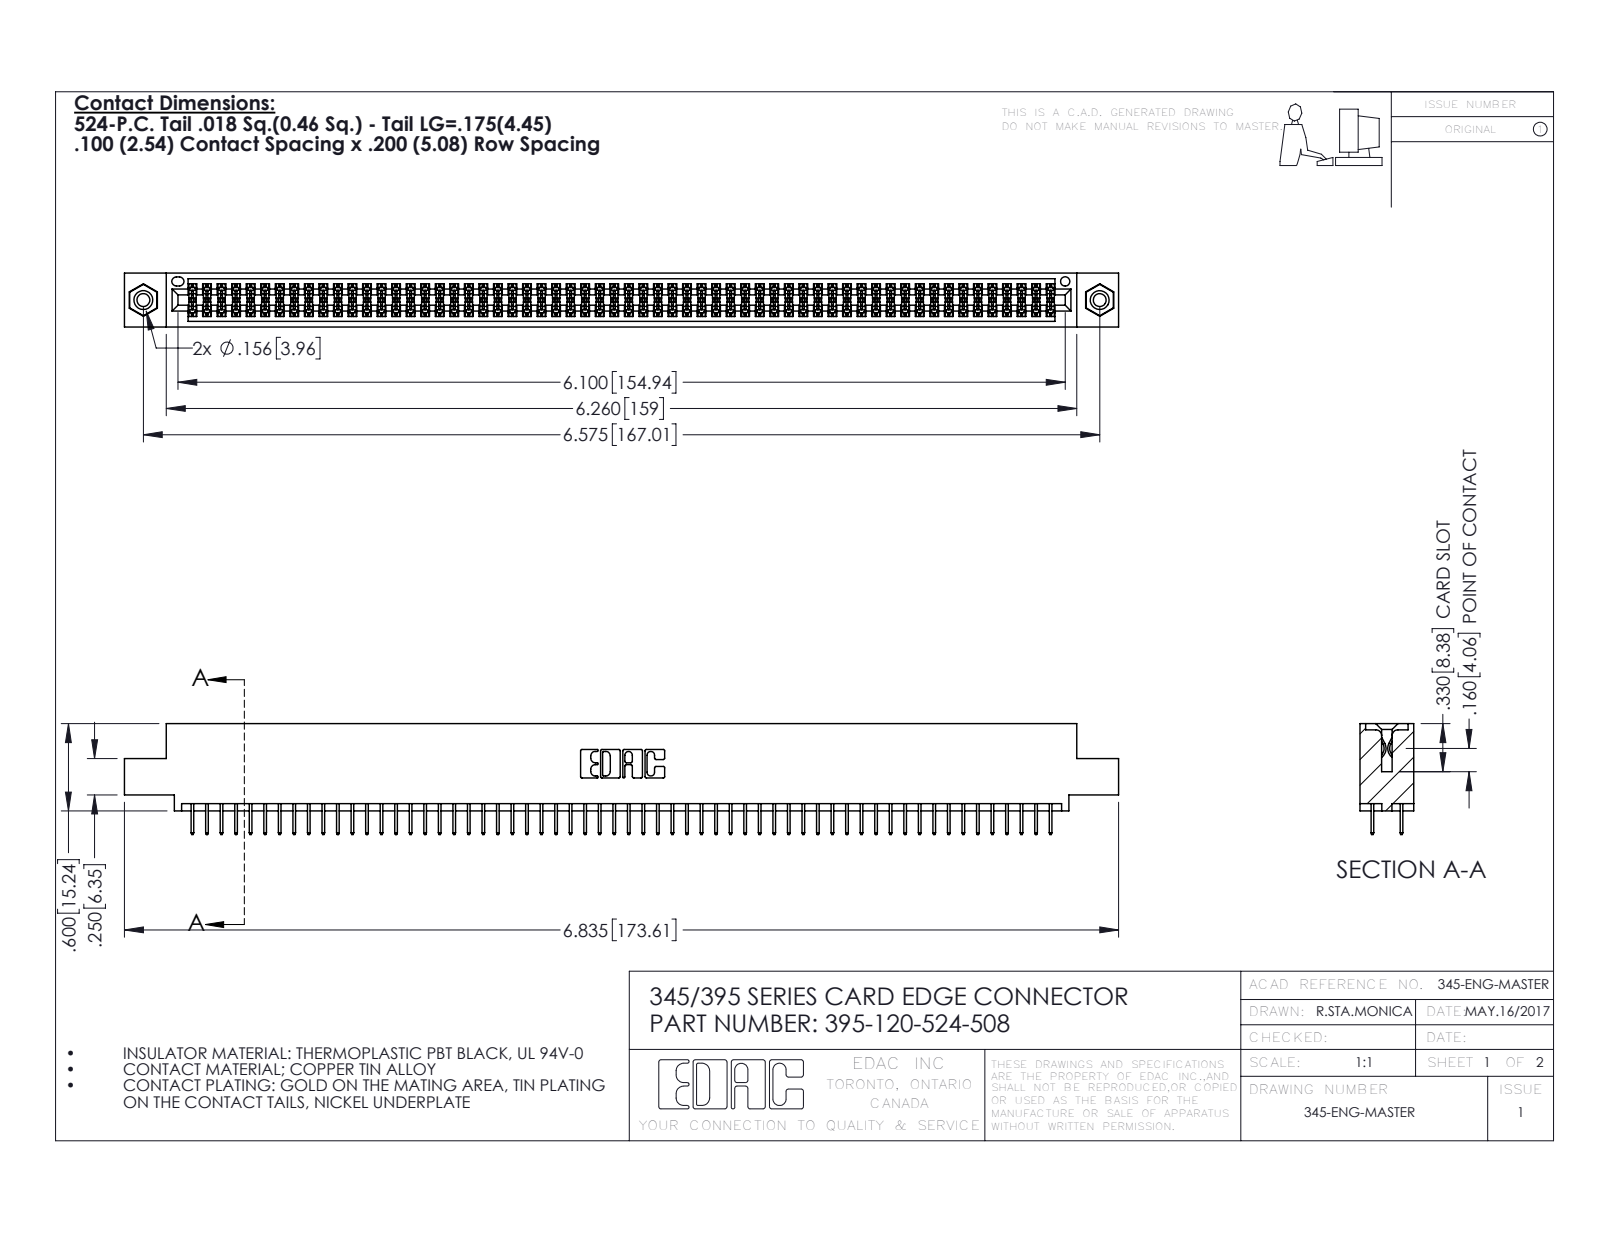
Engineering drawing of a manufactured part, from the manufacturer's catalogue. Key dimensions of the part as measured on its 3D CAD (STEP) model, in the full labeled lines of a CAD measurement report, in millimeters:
Part name (STEP PRODUCT): 345-292-001_345-293-124; 345 Part_0.110 Offset - 0.156 Dia-TI; 345-250-001_345-250-003-102; 395-120-524-508
STEP written by: SolidWorks 2016 (CONFIG_CONTROL_DESIGN)
Units: millimetres
Bodies: 123 solids, 6670 faces (4796 planar, 1858 cylindrical, 16 other)
Overall size (bounding box): 173.6 × 19.4 × 9.4
Volume: 16 760 mm³ · Surface area: 24 770 mm²
Round holes (diameter × count): ⌀2.3 ×2, ⌀3.2 ×2, ⌀4 ×2, ⌀1.6 ×1
Round bosses / shafts (diameter × count): ⌀3.9 ×2
Partial cylindrical surfaces — rounded edges, fillets, slot ends (radius × count): R0.2 ×180, R0.3 ×22, R0.2 ×6, R0.8 ×6, R0.7 ×3, R0.4 ×2, R0.5 ×2, R0.6 ×2
Main face-to-face distances: 1.8, 7.6, 5.1, 9.4, 2.5, 6.9, 0.6, 5.7, 1.8, 4.4
Hole centre spacings: 6.9, 161, 167
